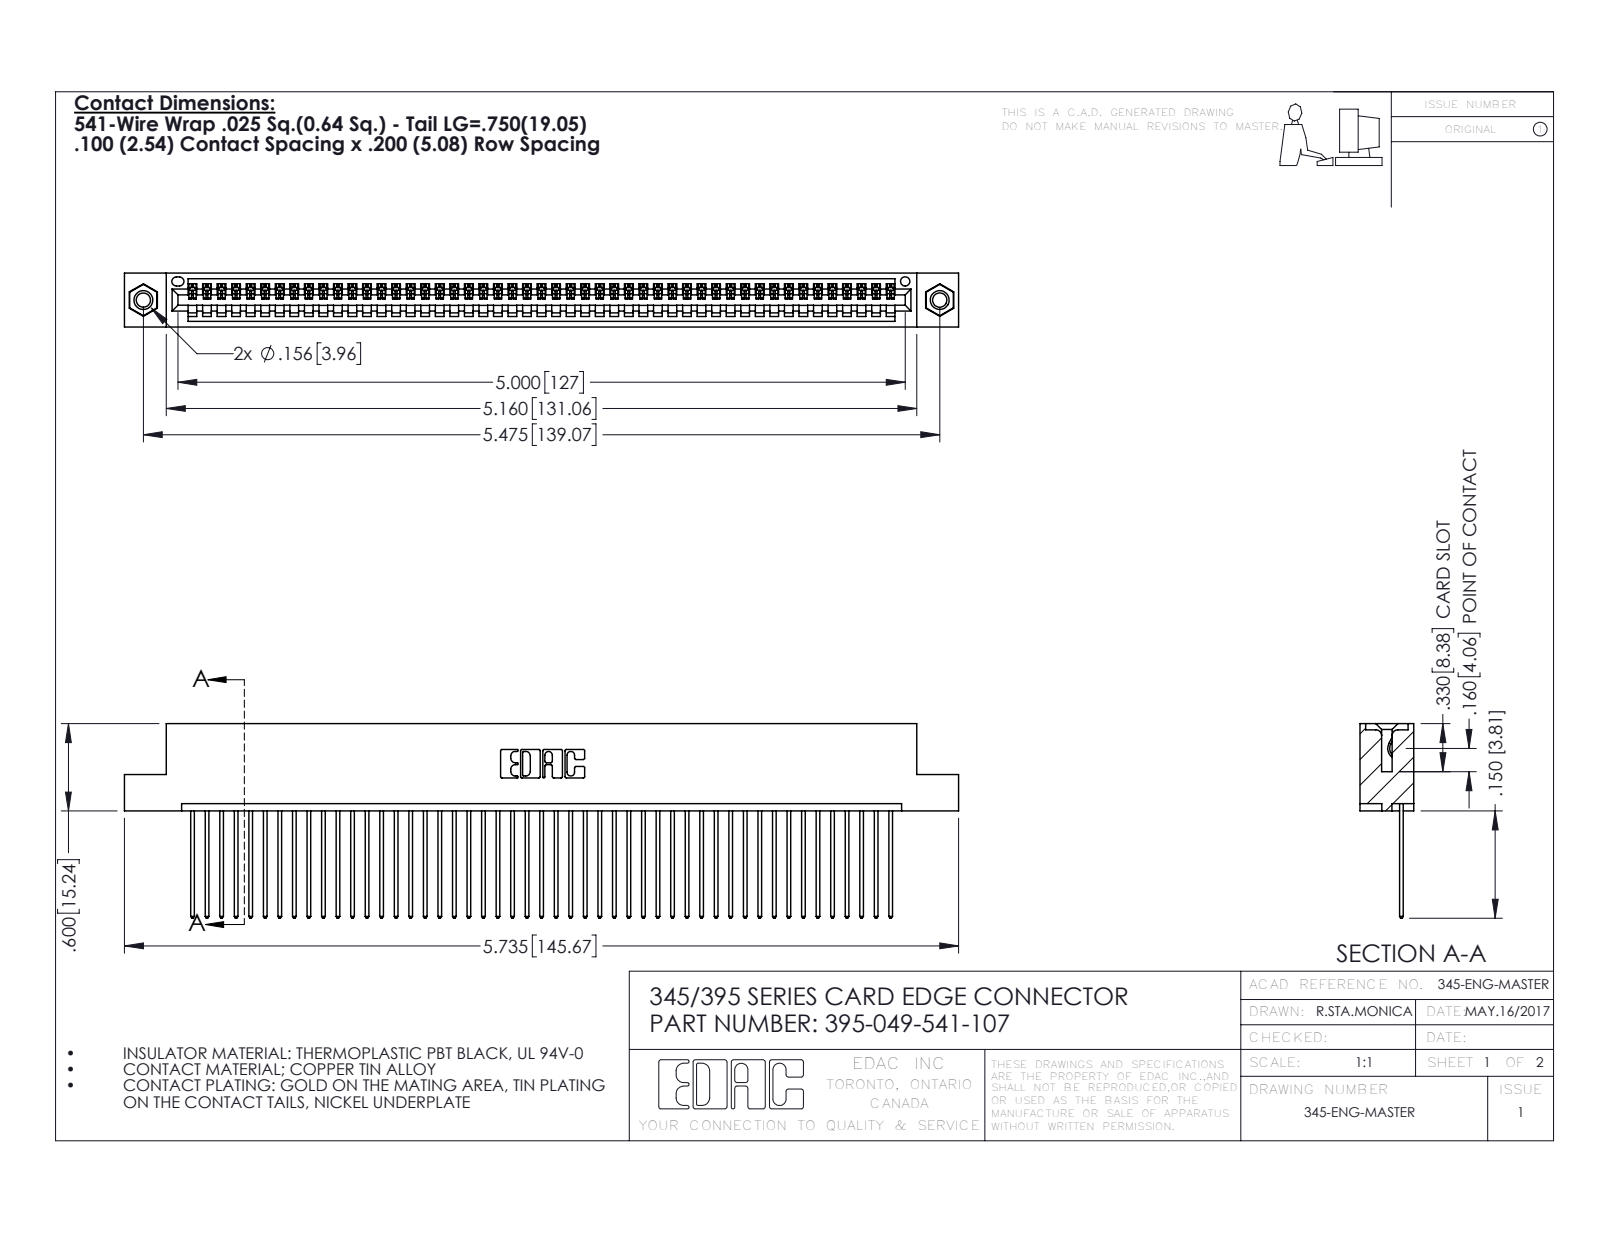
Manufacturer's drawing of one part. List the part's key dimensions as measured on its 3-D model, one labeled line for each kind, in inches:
Part name (STEP PRODUCT): 345 Part_Flush Mounting Lugs - 0.156 Dia-TI; 345-250-001_345-250-005-103; 395-049-541-107; 345-292-001_345-293-141
STEP written by: SolidWorks 2016 (CONFIG_CONTROL_DESIGN)
Units: inches
Bodies: 52 solids, 3028 faces (2072 planar, 940 cylindrical, 16 other)
Overall size (bounding box): 5.735 × 1.337 × 0.37
Volume: 0.857 in³ · Surface area: 30.6 in²
Round holes (diameter × count): ⌀0.098 ×2, ⌀0.125 ×2, ⌀0.156 ×2, ⌀0.064 ×1
Round bosses / shafts (diameter × count): ⌀0.155 ×2
Partial cylindrical surfaces — rounded edges, fillets, slot ends (radius × count): R0.006 ×98, R0.01 ×98, R0.01 ×22, R0.007 ×6, R0.031 ×6, R0.026 ×3, R0.031 ×2, R0.04 ×2
Main face-to-face distances: 0.072, 0.298, 0.098, 0.272, 0.025, 0.37, 0.2, 0.225, 0.149, 0.072
Hole centre spacings: 0.27, 5.239, 5.475
